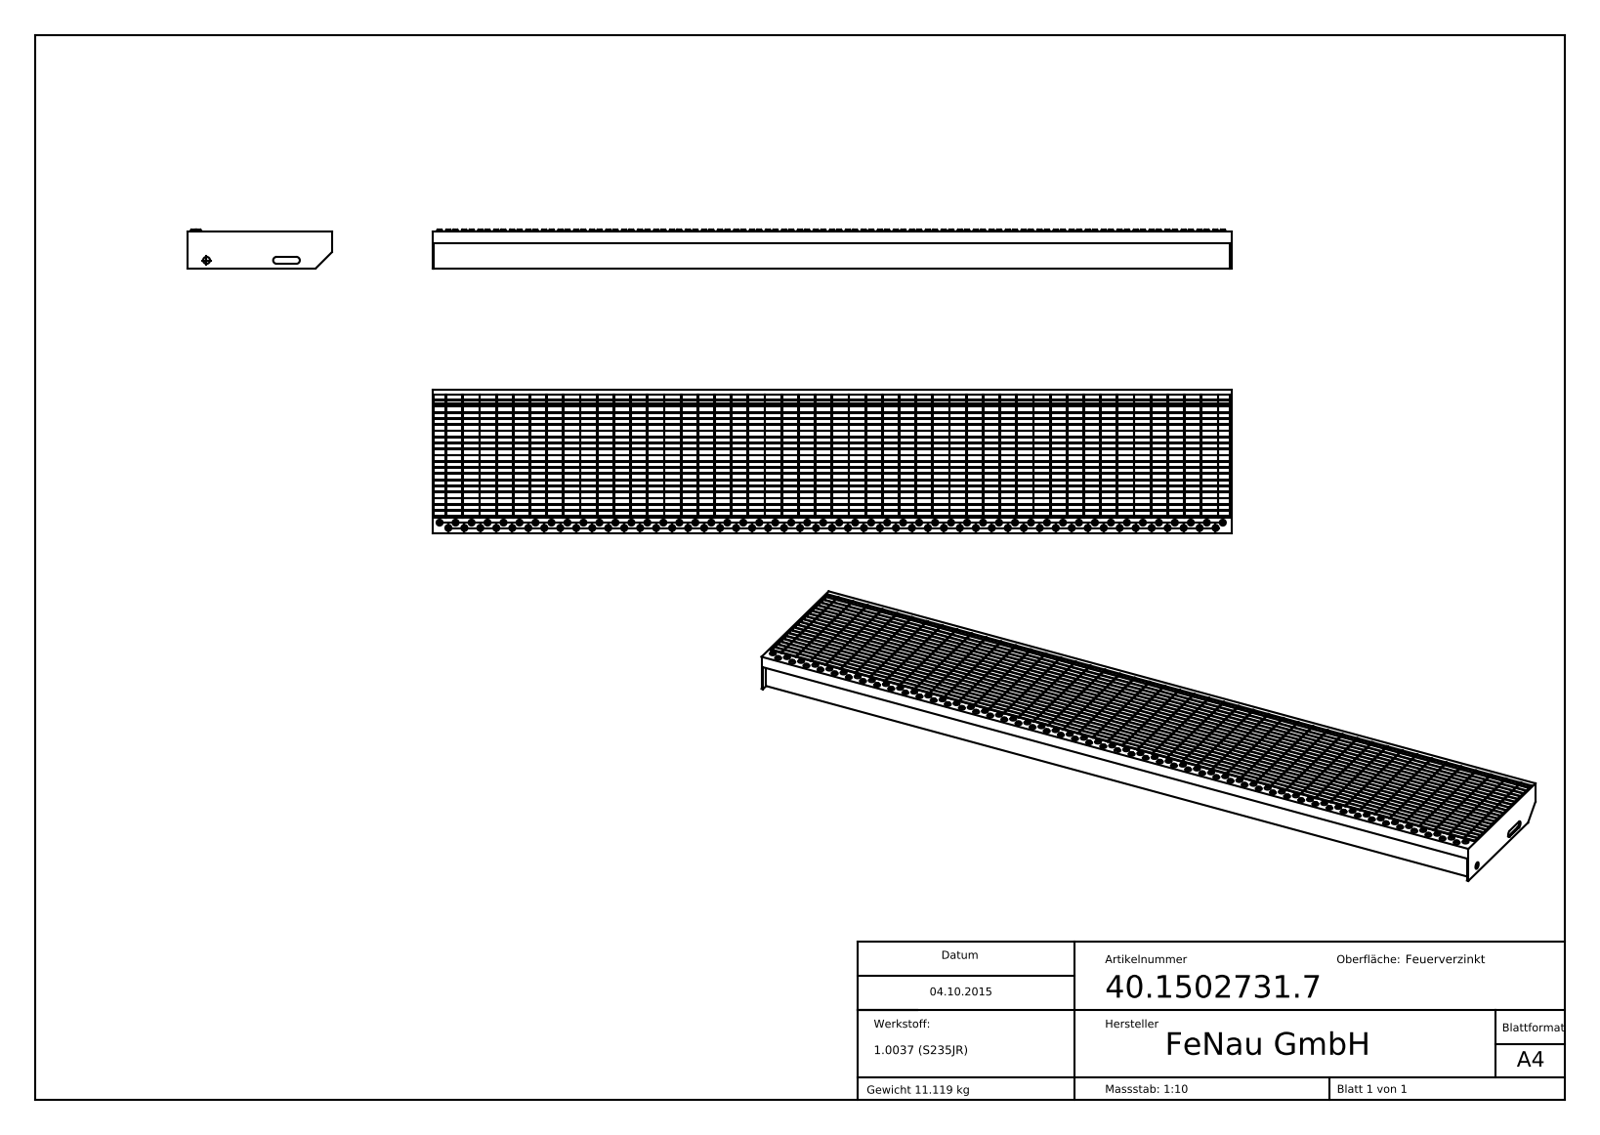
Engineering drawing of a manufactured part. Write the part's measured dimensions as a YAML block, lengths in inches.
part_name: "40.1502731.7"
step_written_by: "SolidWorks 2015 (CONFIG_CONTROL_DESIGN)"
units: inches
bodies: {solids: 59, faces: 1329, planar: 844, cylindrical: 208, other: 277}
overall_size: [59.055, 10.63, 2.861]
volume: 86.96
surface_area: 2764
round_holes:
  - {diameter: 0.276, count: 99}
  - {diameter: 0.512, count: 1}
partial_cylinders:
  - {radius: 0.256, count: 2}
face_to_face_distances: [0.079, 0.512, 0.453, 0.059, 0.906, 0.787, 9.705, 1.24, 1.299, 1.358]
hole_center_spacings: [1.181, 2.362, 3.543, 4.724, 5.906, 7.087, 8.268, 9.449]
